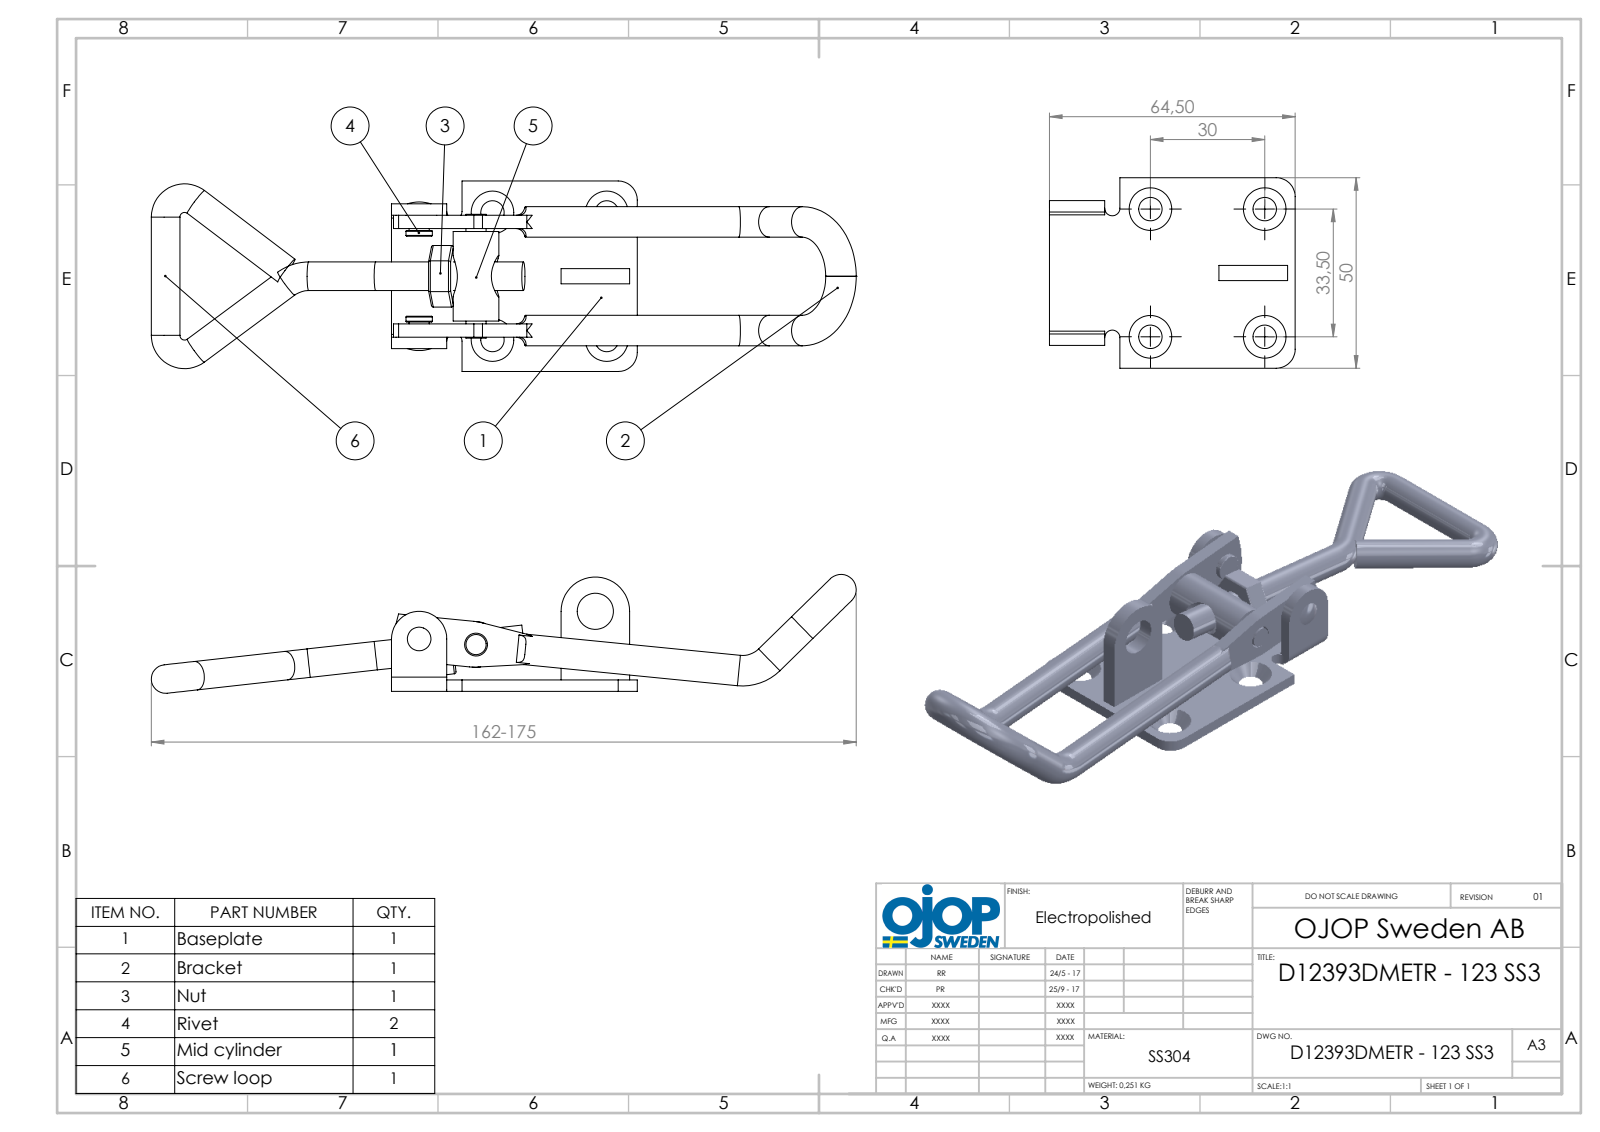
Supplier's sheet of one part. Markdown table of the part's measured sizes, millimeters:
| quantity | value |
| --- | --- |
| part name | nit; skruvögla; mutter; rulle (+3 more) |
| STEP written by | SolidWorks 2015 (AUTOMOTIVE_DESIGN) |
| units | millimeters |
| bodies | 7 solids, 197 faces (63 planar, 86 cylindrical, 48 other) |
| overall size | 185.04 × 50 × 31.2 |
| volume | 34 547 mm³ |
| surface area | 22 625 mm² |
| round holes (diameter × count) | 5.5 × 1, 6 × 1, 6.8 × 1, 7.6 × 1, 9.5 × 1 |
| round bosses / shafts (diameter × count) | 8 × 5, 7.5 × 4, 5.3 × 2, 12 × 1, 7.51 × 1, 6.9 × 1 |
| partial cylindrical surfaces (radius × count) | 0.5 × 12, 2 × 6, 0.74 × 2, 3.74 × 2, 5 × 2, 15 × 2, 7.25 × 1, 9 × 1 |
| main face-to-face distances | 3, 14, 18, 14.5, 3.5, 28.5, 10.5, 32, 21, 4 |
| hole center spacings | 15, 32.51, 46.81 |
